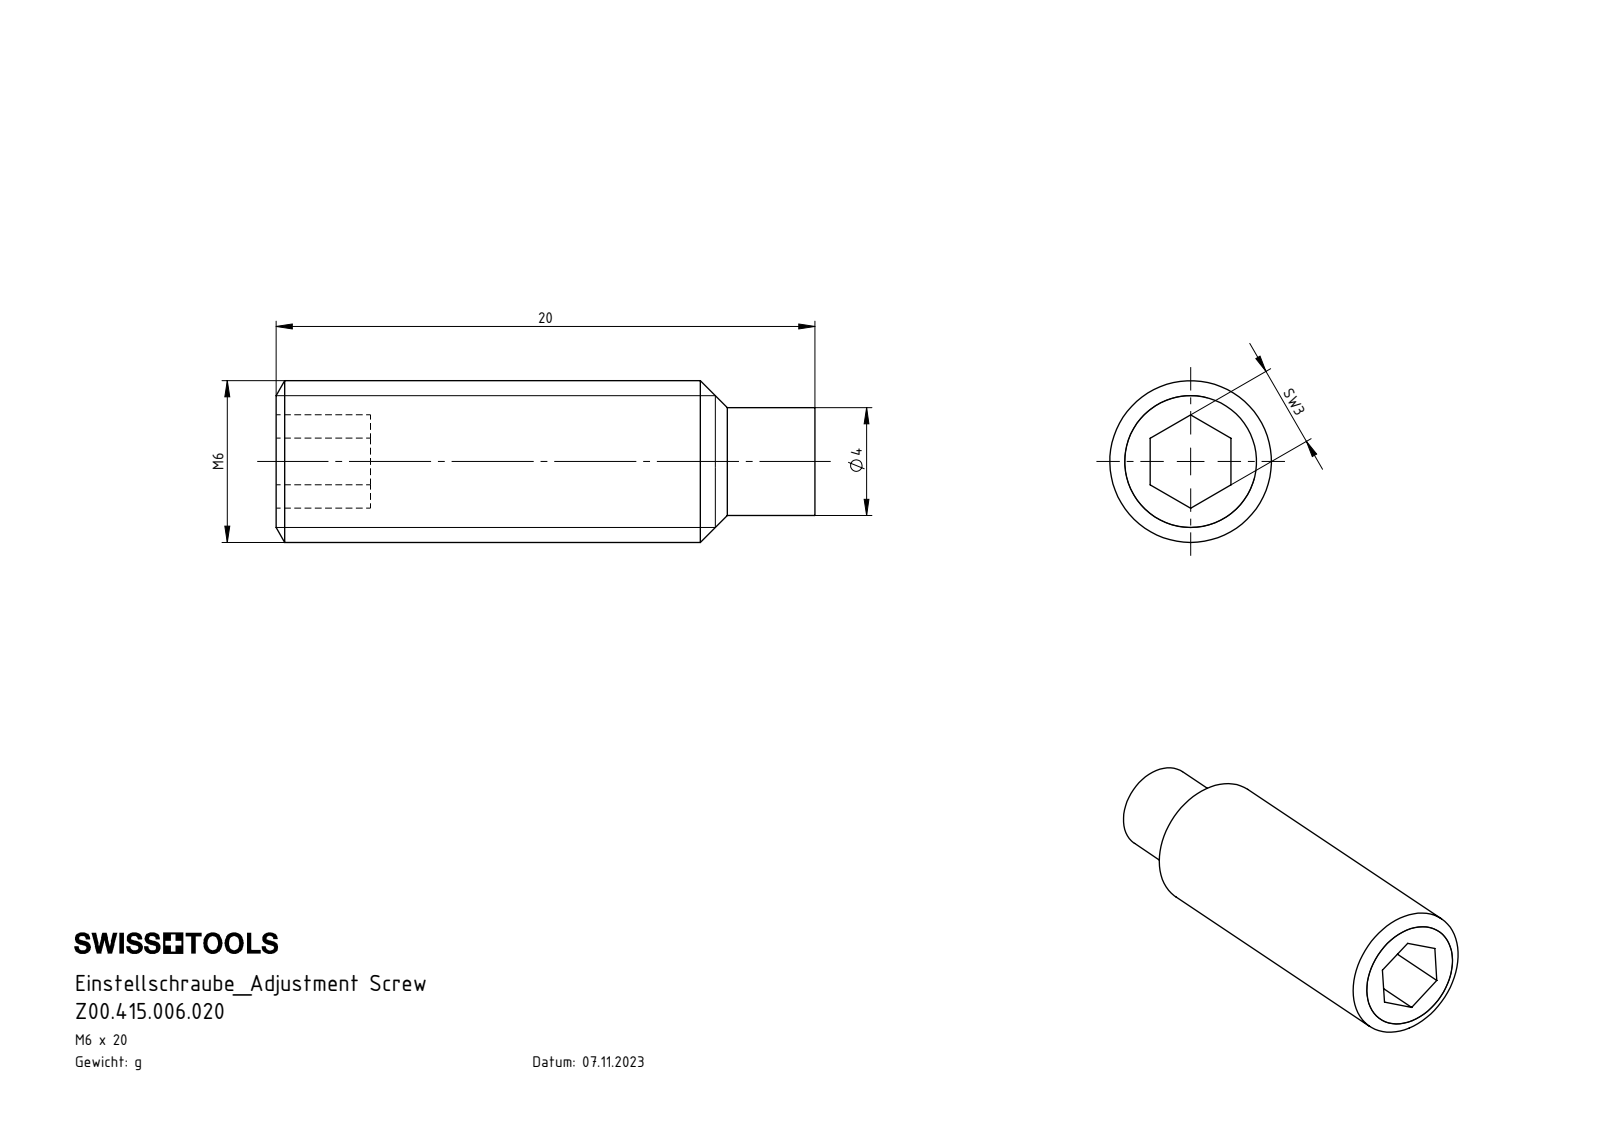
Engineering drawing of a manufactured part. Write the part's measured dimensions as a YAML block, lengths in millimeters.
part_name: "Z00.415.006.020"
step_written_by: "SolidWorks 2022 (AUTOMOTIVE_DESIGN)"
units: millimeters
bodies: {solids: 1, faces: 17, planar: 9, cylindrical: 4, other: 4}
overall_size: [20, 6, 6]
volume: 477
surface_area: 433
round_bosses_or_shafts:
  - {diameter: 6, count: 1}
  - {diameter: 4, count: 1}
face_to_face_distances: [3, 20, 3.5, 16.5]
